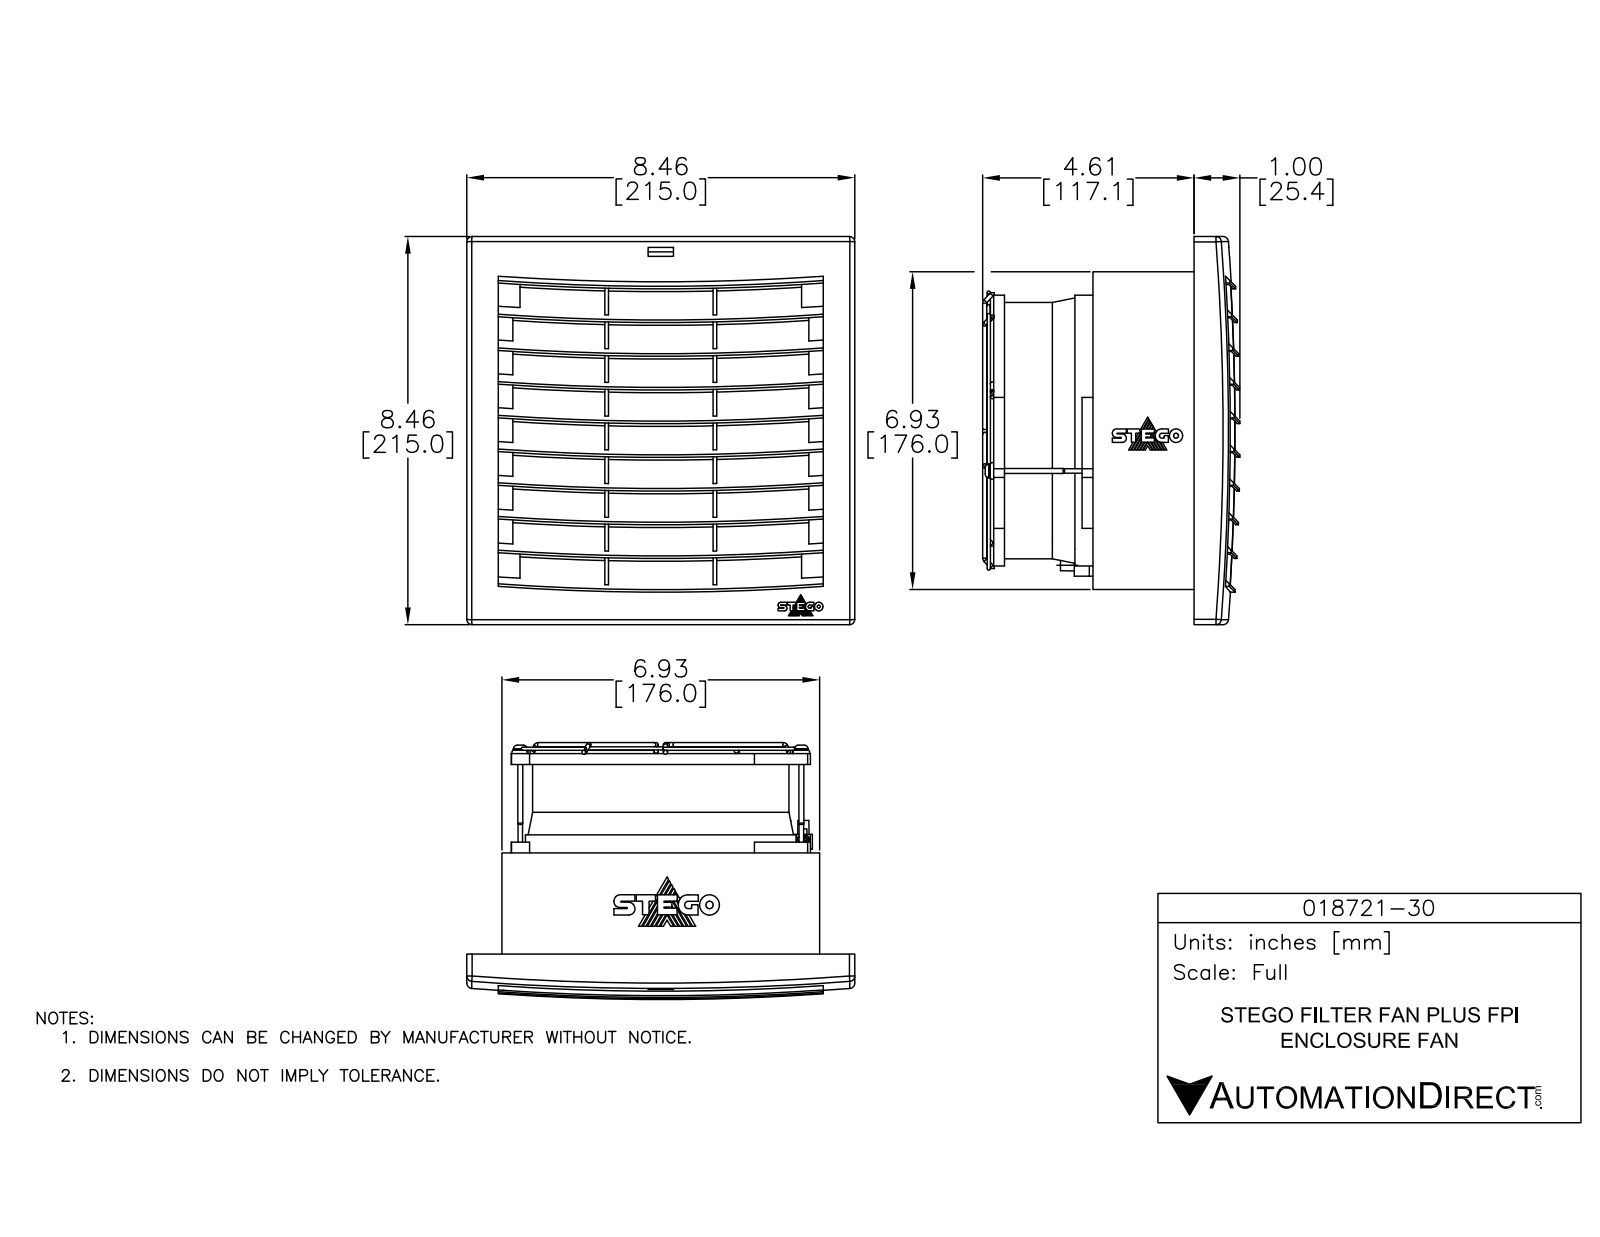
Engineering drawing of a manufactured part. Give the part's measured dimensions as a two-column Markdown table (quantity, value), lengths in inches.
| quantity | value |
| --- | --- |
| part name | PRODUCT_NAME_1 |
| STEP written by | ACIS (AUTOMOTIVE_DESIGN_CC2) |
| units | inches |
| bodies | 1 solid, 800 faces (442 planar, 356 cylindrical, 2 other) |
| overall size | 8.465 × 8.465 × 5.591 |
| volume | 96.36 in³ |
| surface area | 663.8 in² |
| round holes (diameter × count) | 1.381 × 1, 2.024 × 1, 2.666 × 1, 3.121 × 1, 3.309 × 1, 3.951 × 1, 4.005 × 1, 4.594 × 1, 4.888 × 1, 5.354 × 1, 5.89 × 1 |
| round bosses / shafts (diameter × count) | 6.358 × 1, 6.024 × 1, 5.124 × 1, 4.83 × 1, 4.241 × 1, 4.187 × 1, 3.545 × 1, 3.357 × 1 |
| partial cylindrical surfaces (radius × count) | 27.614 × 19, 2.463 × 5, 0.197 × 4, 0.201 × 4, 0.551 × 2, 0.736 × 1, 1.119 × 1, 1.237 × 1 |
| main face-to-face distances | 0.941, 1.881, 0.118, 0.059, 0.173, 6.756, 0.47, 0.508, 0.47, 1 |
